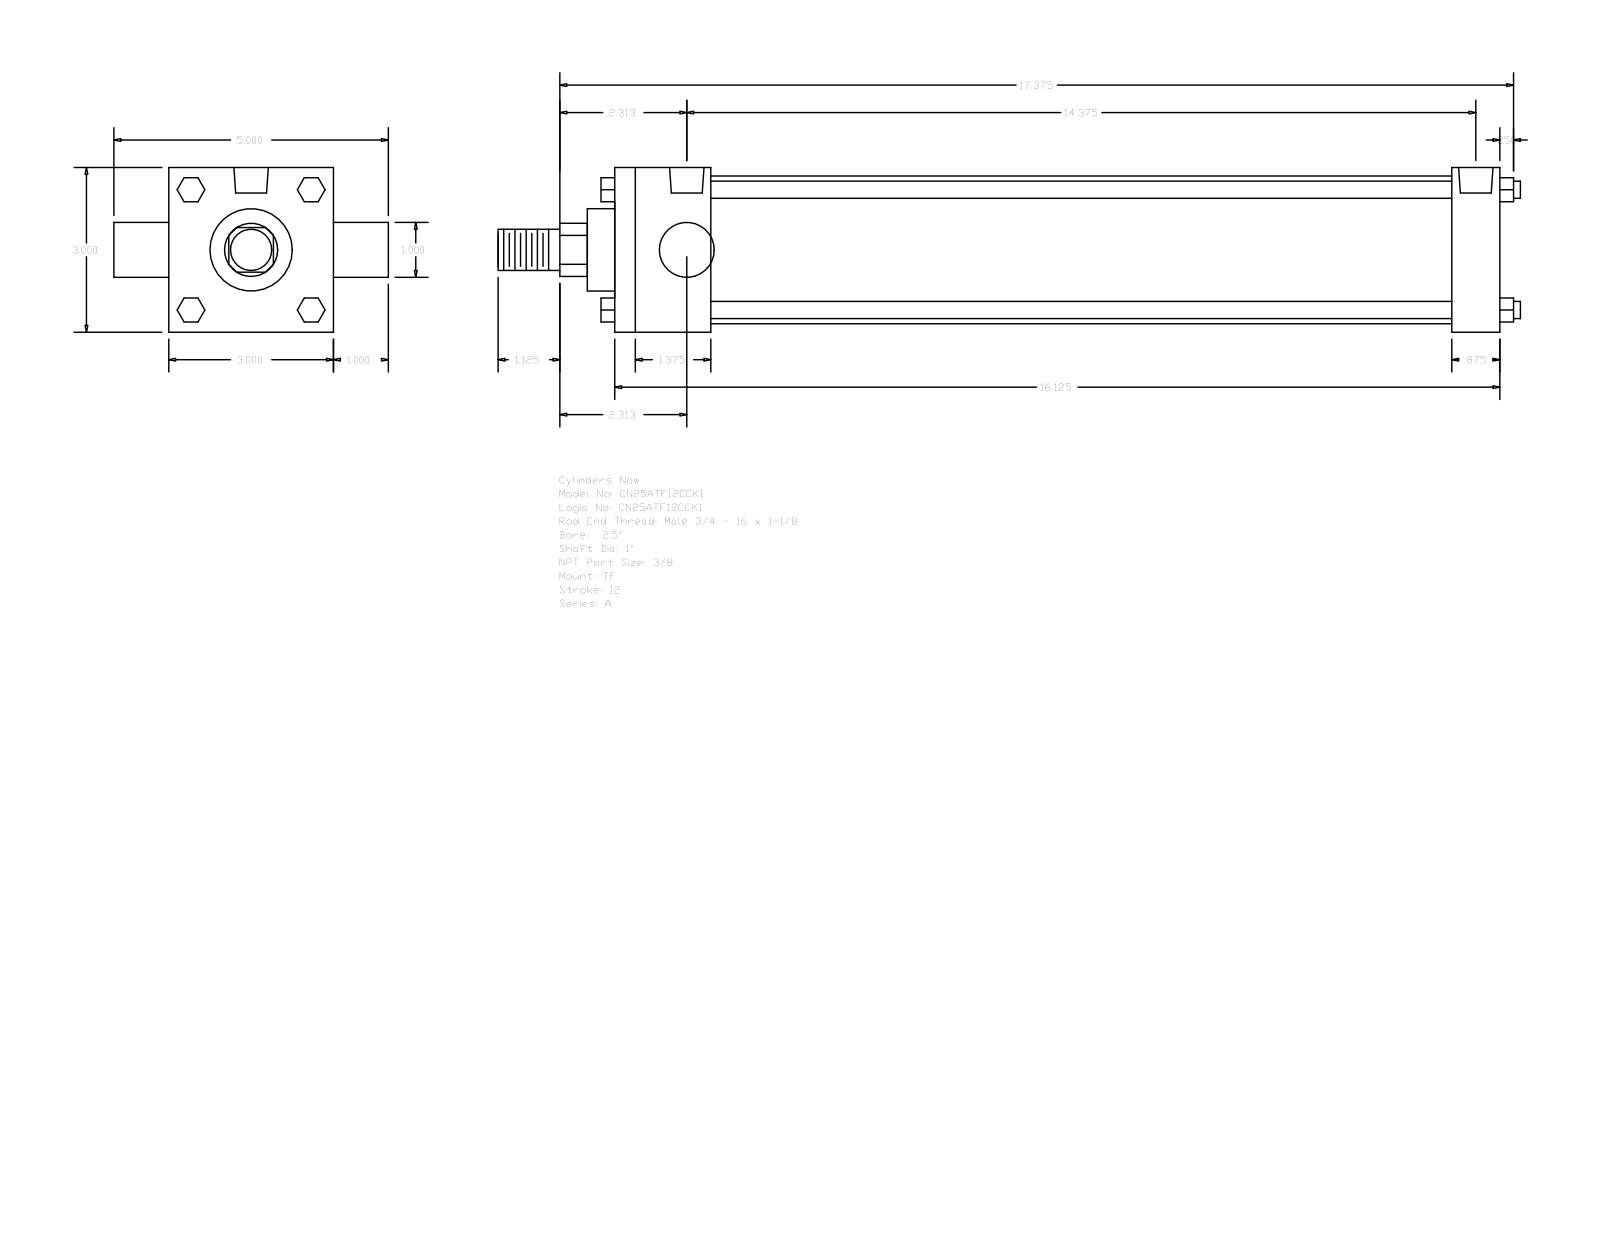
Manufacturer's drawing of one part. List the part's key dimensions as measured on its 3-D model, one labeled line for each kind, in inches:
Part name (STEP PRODUCT): A_TF__0250_1
STEP written by: GSSL Pune (CONFIG_CONTROL_DESIGN)
Units: inches
Bodies: 0 solids, 120 faces (92 planar, 28 cylindrical, 0 other)
Overall size (bounding box): 18.625 × 5 × 3
Round holes (diameter × count): ⌀0.219 ×3, ⌀0.627 ×2
Round bosses / shafts (diameter × count): ⌀0.313 ×4, ⌀1 ×2, ⌀2.69 ×1, ⌀1.5 ×1, ⌀0.75 ×1
Partial cylindrical surfaces — rounded edges, fillets, slot ends (radius × count): R0.484 ×1
Main face-to-face distances: 3, 16.125, 1.75, 15.25, 13.5, 14.375, 0.875, 1, 4, 0.5
Hole centre spacings: 0.094, 14.469, 14.375, 14.562
